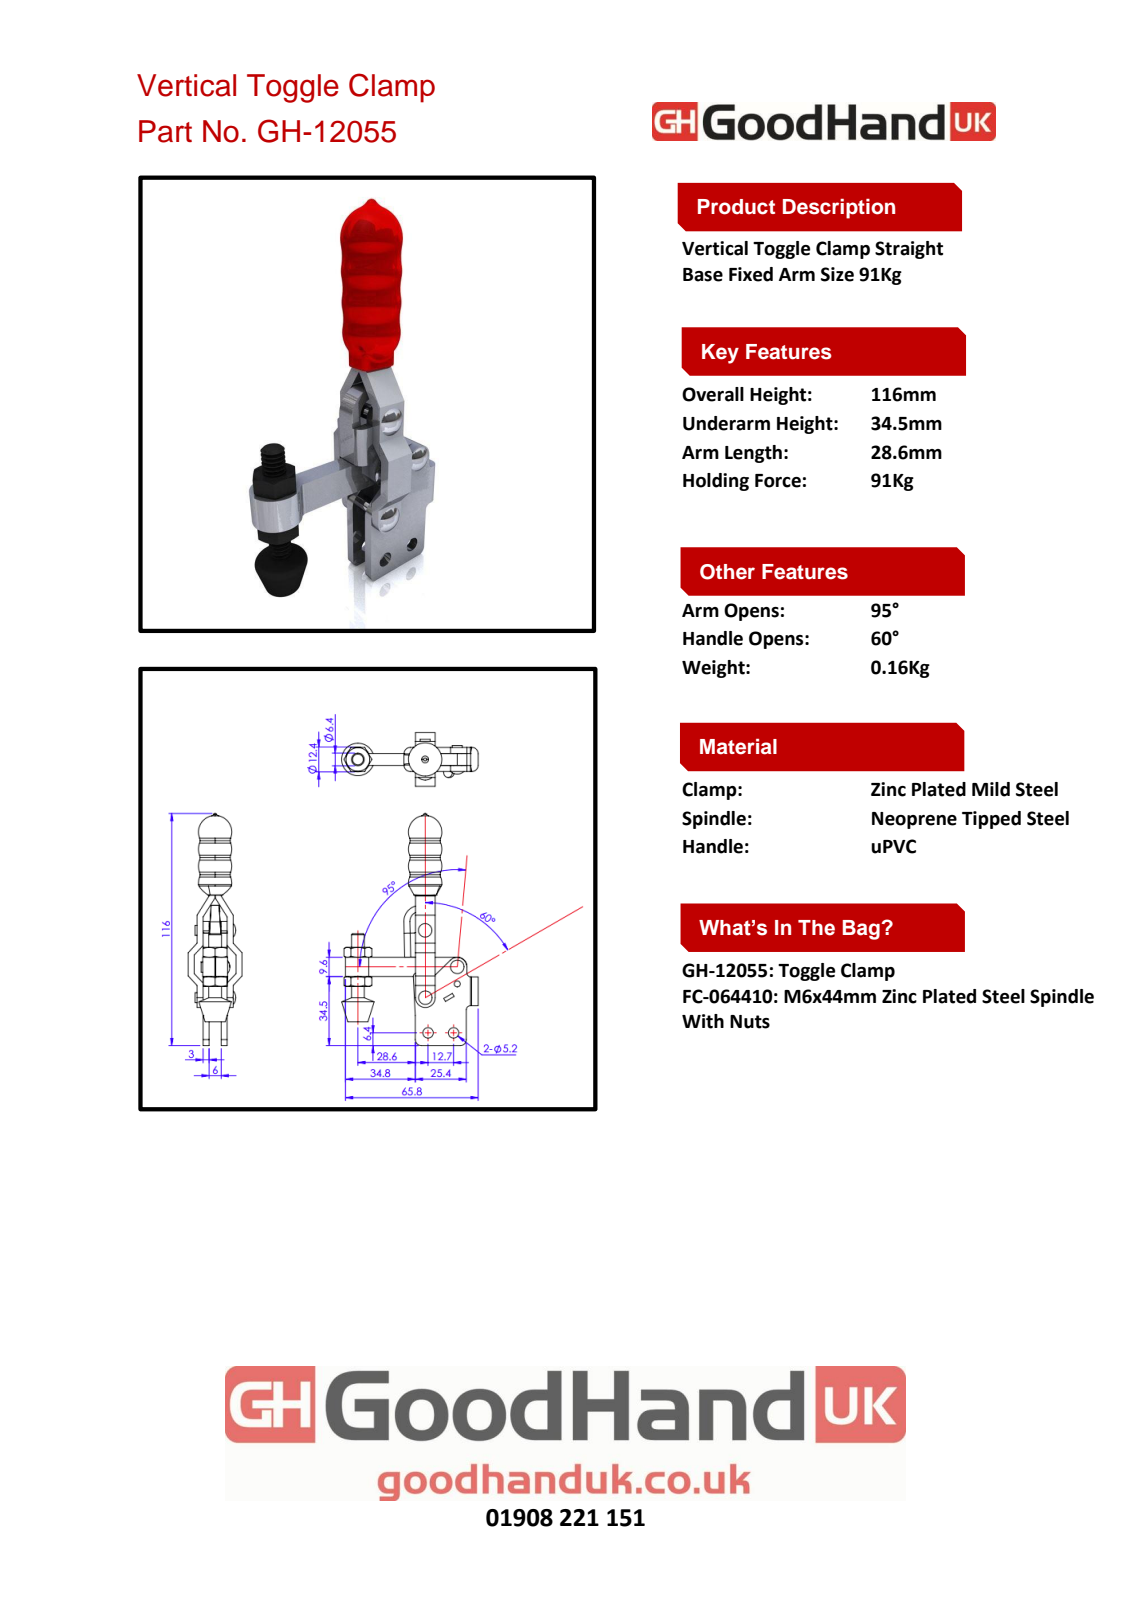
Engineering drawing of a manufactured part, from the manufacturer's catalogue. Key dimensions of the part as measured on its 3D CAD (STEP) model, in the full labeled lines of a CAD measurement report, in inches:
Part name (STEP PRODUCT): 11205001-1^EMC12055; Group1^EMC12055; Group5^EMC12055; Group2^EMC12055 (+3 more)
STEP written by: SolidWorks 2016 (AUTOMOTIVE_DESIGN)
Units: inches
Bodies: 6 solids, 270 faces (111 planar, 98 cylindrical, 61 other)
Overall size (bounding box): 4.567 × 2.677 × 1.055
Volume: 1.699 in³ · Surface area: 28.4 in²
Round holes (diameter × count): ⌀0.138 ×4, ⌀0.205 ×2, ⌀0.252 ×1
Round bosses / shafts (diameter × count): ⌀0.197 ×4, ⌀0.157 ×4, ⌀0.488 ×1, ⌀0.25 ×1
Partial cylindrical surfaces — rounded edges, fillets, slot ends (radius × count): R0.079 ×4, R0.123 ×4, R0.004 ×2, R0.039 ×2, R0.118 ×2, R0.122 ×2, R0.177 ×2, R0.189 ×2
Main face-to-face distances: 0.118, 0.354, 0.236, 0.472, 0.591, 0.386, 0.173, 0.291, 0.409, 0.528
Hole centre spacings: 0.5, 0.598, 0.614, 0.694, 0.724, 0.87, 0.886, 0.955
